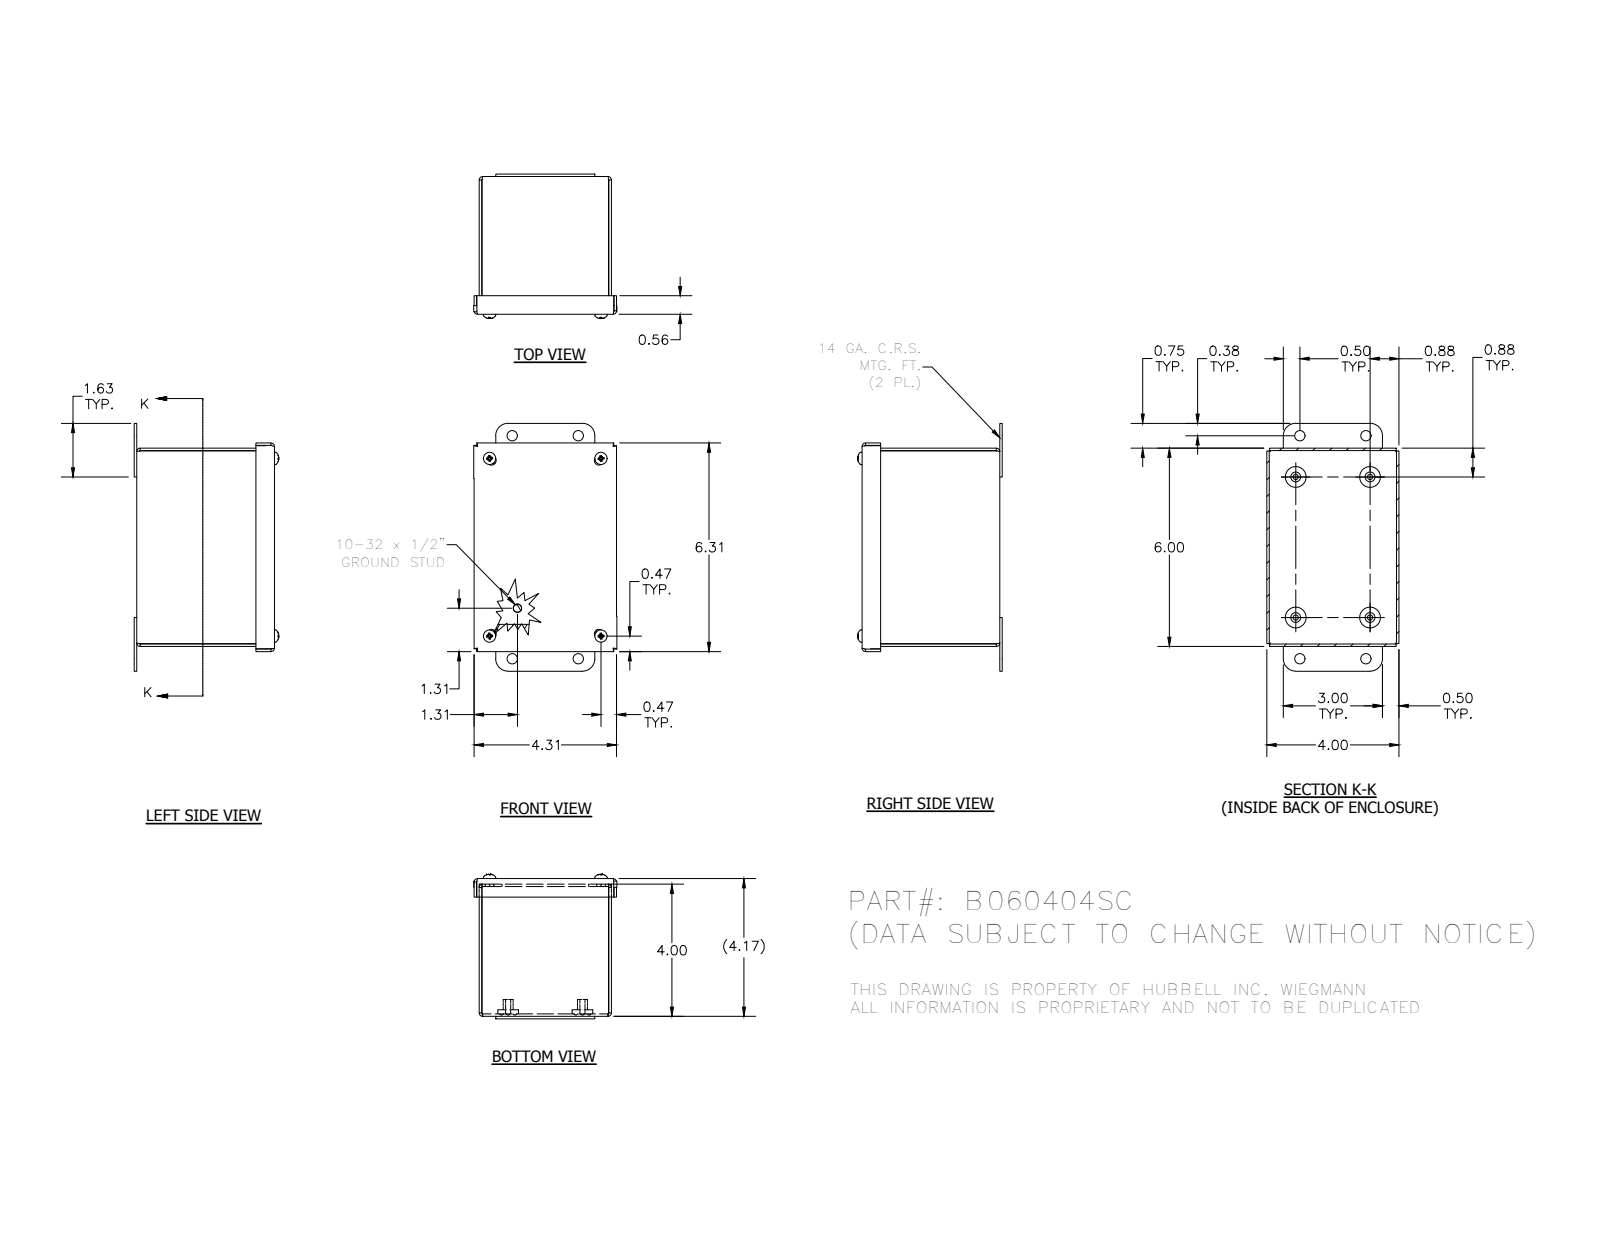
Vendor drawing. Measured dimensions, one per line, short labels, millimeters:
name: B060404SC; 3481; 34984; B060404SCBKP (+6 more)
written by: Autodesk Inventor 2012 (AUTOMOTIVE_DESIGN)
unit: mm
bodies: 23 solids, 532 faces (311 planar, 102 cylindrical, 119 other)
size: 190.5 × 110.4 × 110.1
volume: 221 700 mm³; area: 226 100 mm²
holes: 4× ⌀3.7, 4× ⌀4, 4× ⌀5, 4× ⌀7.1, 4× ⌀7.1, 4× ⌀7.9, 4× ⌀8
bosses: 5× ⌀4.8, 4× ⌀15.9, 4× ⌀11.5, 4× ⌀10.3, 4× ⌀9.5, 4× ⌀7.6, 4× ⌀6.3, 1× ⌀6.4
rounds: 12× R0.8, 12× R2.7, 4× R2.3, 4× R9.5
face distances: 1.9, 104, 99.7, 150.5, 101.6, 97.8, 105.9, 102.1, 152.4, 148.6
hole spacings: 84.2, 135, 137, 2.2, 31.9, 70.5, 72.8, 85.7
